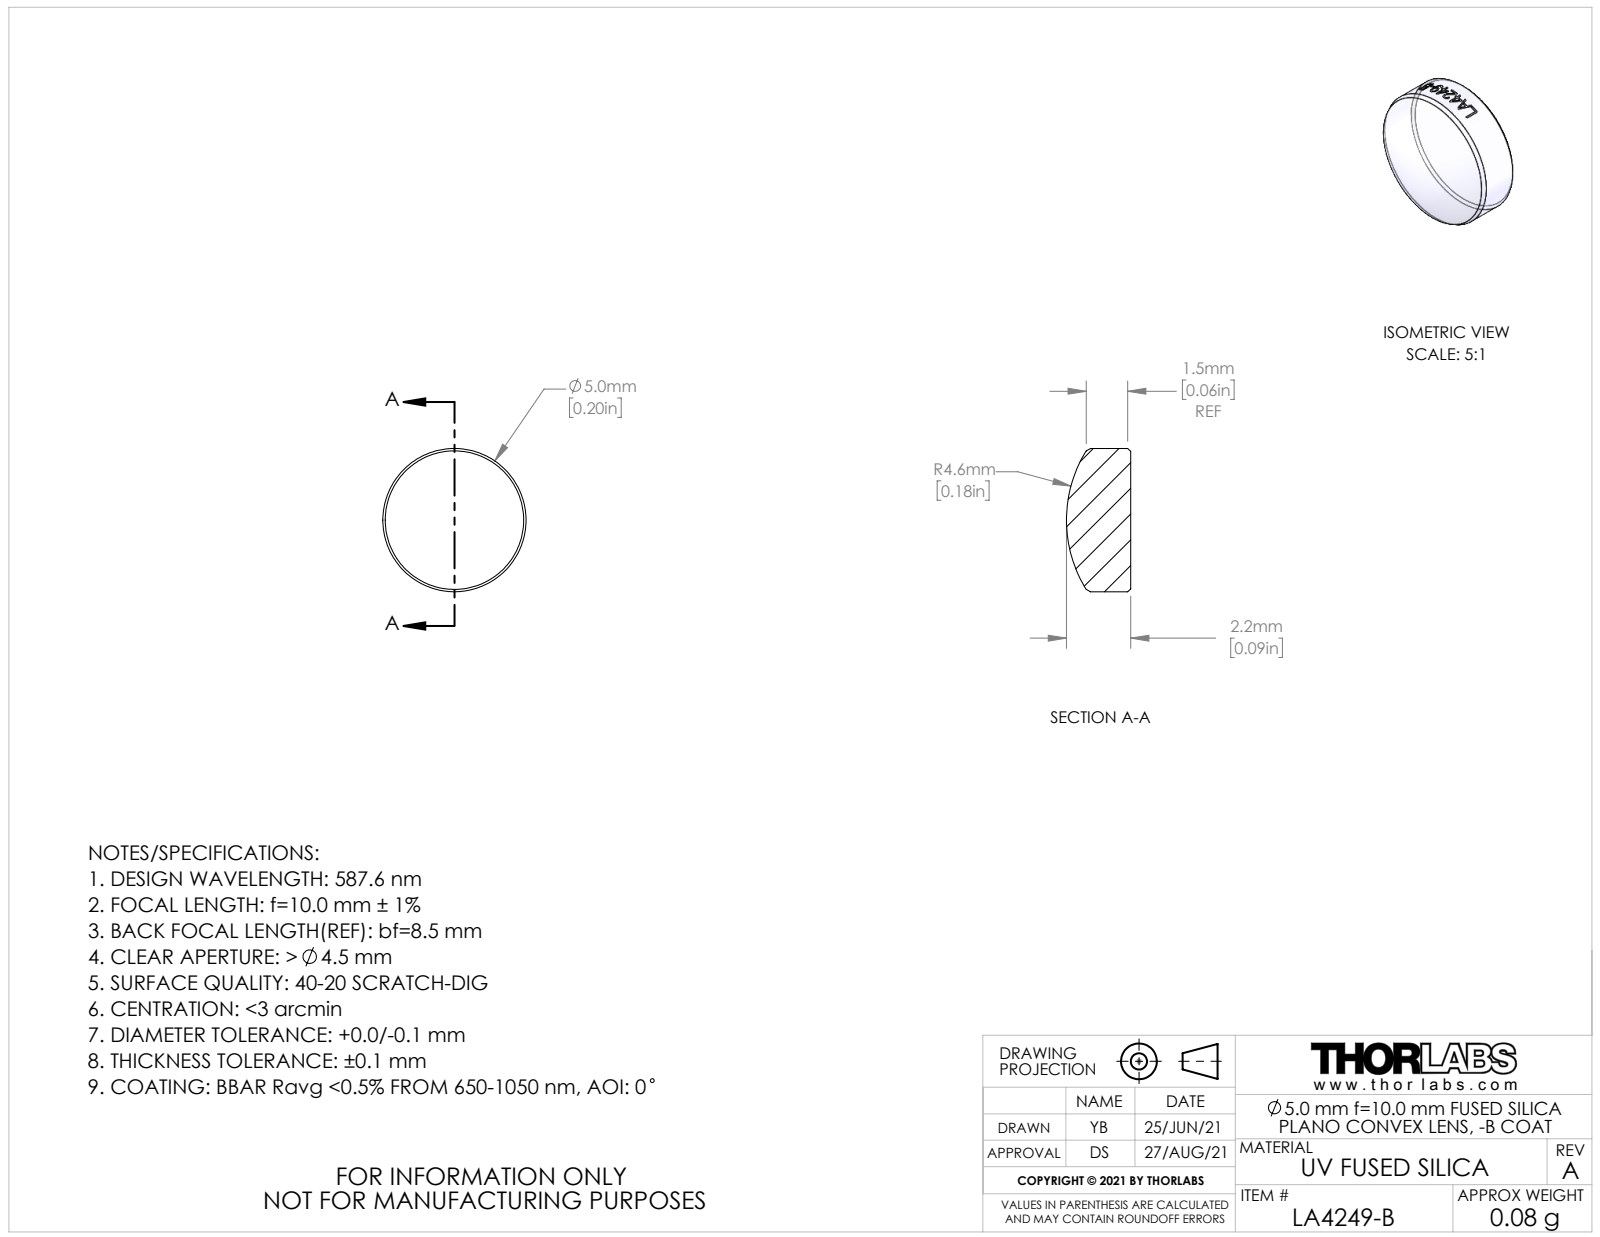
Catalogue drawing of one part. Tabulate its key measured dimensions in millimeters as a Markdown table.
| quantity | value |
| --- | --- |
| part name | CTN017889-E0W |
| STEP written by | SolidWorks 2018 (AUTOMOTIVE_DESIGN) |
| units | millimeters |
| bodies | 1 solid, 23 faces (1 planar, 16 cylindrical, 6 other) |
| overall size | 5 × 5 × 2.24 |
| volume | 37 mm³ |
| surface area | 63 mm² |
| round bosses / shafts (diameter × count) | 5 × 1 |
